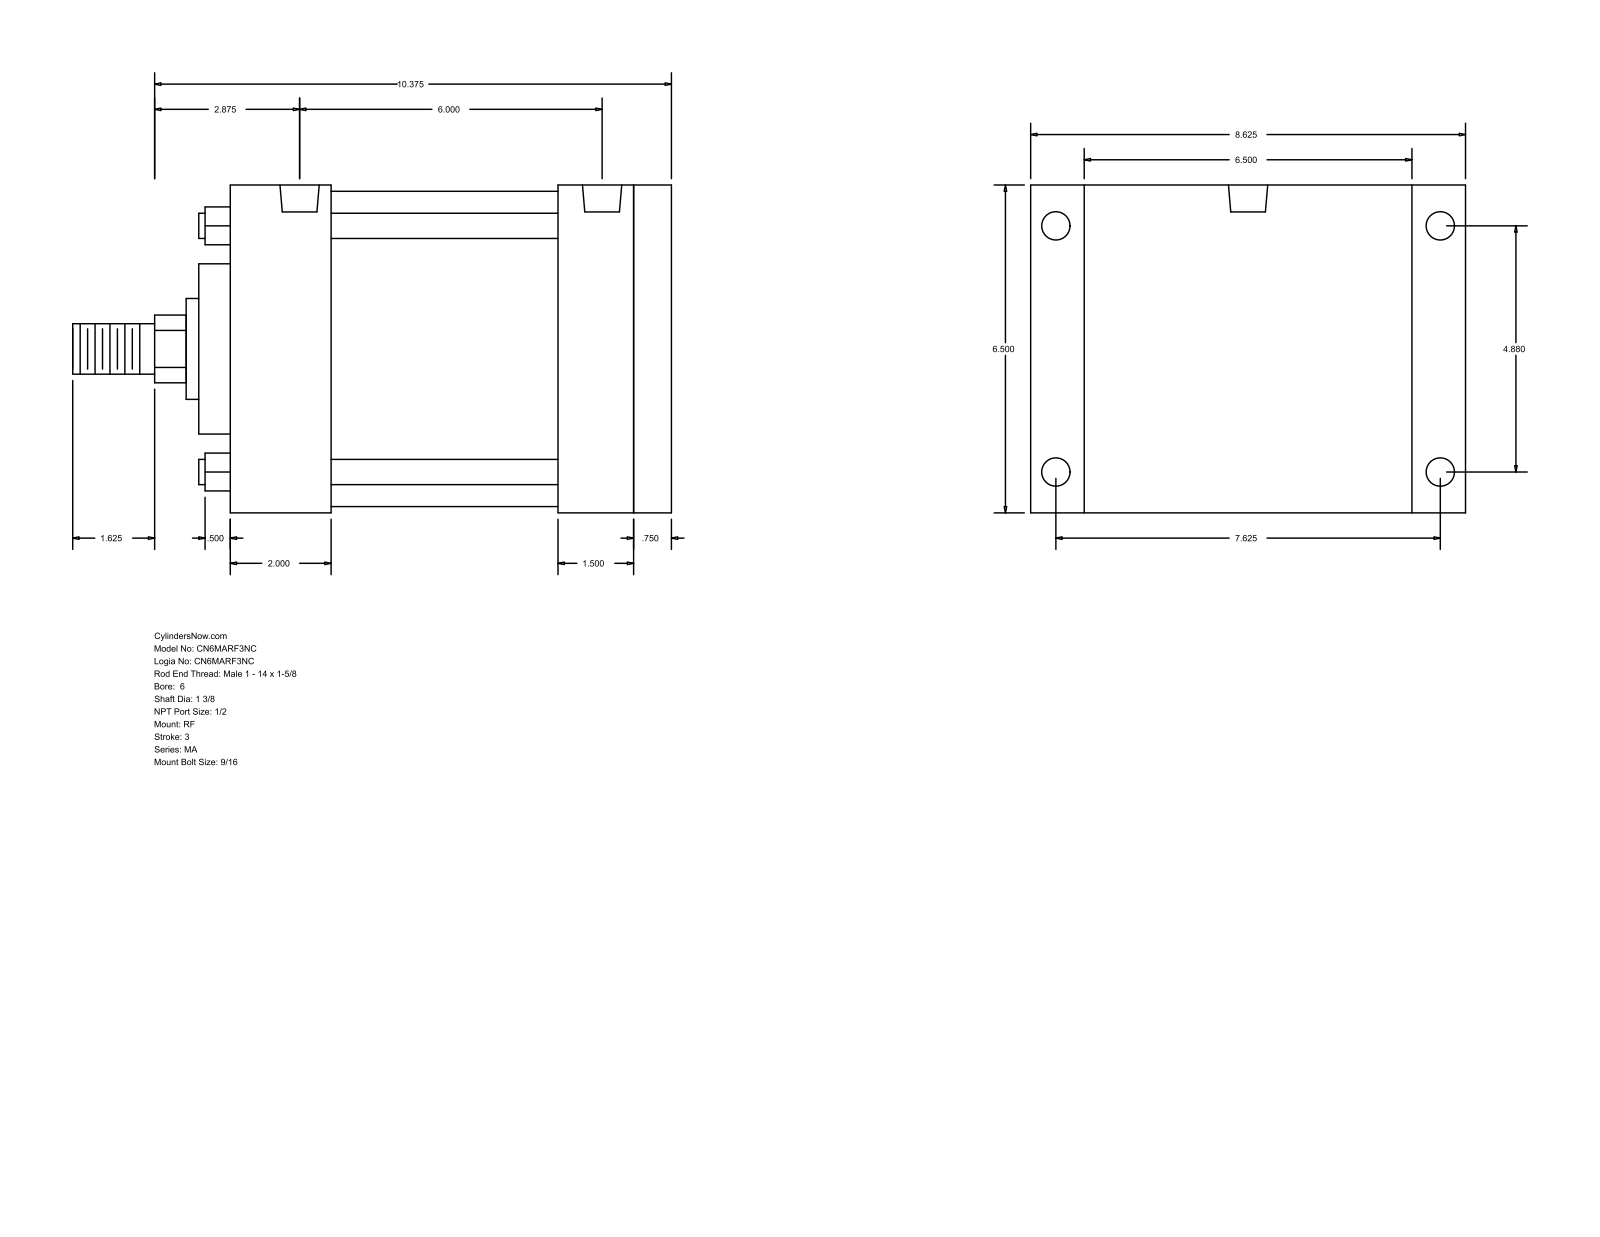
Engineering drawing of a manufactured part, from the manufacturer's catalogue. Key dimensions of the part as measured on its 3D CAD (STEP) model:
Part name (STEP PRODUCT): MA_RF__0600_1.375
STEP written by: GSSL Pune (CONFIG_CONTROL_DESIGN)
Units: millimetres
Bodies: 0 solids, 94 faces (65 planar, 29 cylindrical, 0 other)
Overall size (bounding box): 304.8 × 219.07 × 165.1
Round holes (diameter × count): ⌀14.29 ×4, ⌀17.46 ×4, ⌀19.77 ×2
Round bosses / shafts (diameter × count): ⌀12.7 ×4, ⌀158.75 ×1, ⌀85.72 ×1, ⌀50.8 ×1, ⌀34.92 ×1, ⌀25.4 ×1
Partial cylindrical surfaces — rounded edges, fillets, slot ends (radius × count): R17.06 ×1
Main face-to-face distances: 165.1, 225.42, 19.05, 206.37, 50.8, 155.57, 174.62, 168.28, 117.48, 38.09
Hole centre spacings: 123.96, 155.58, 193.68, 229.95, 3.18, 152.4
